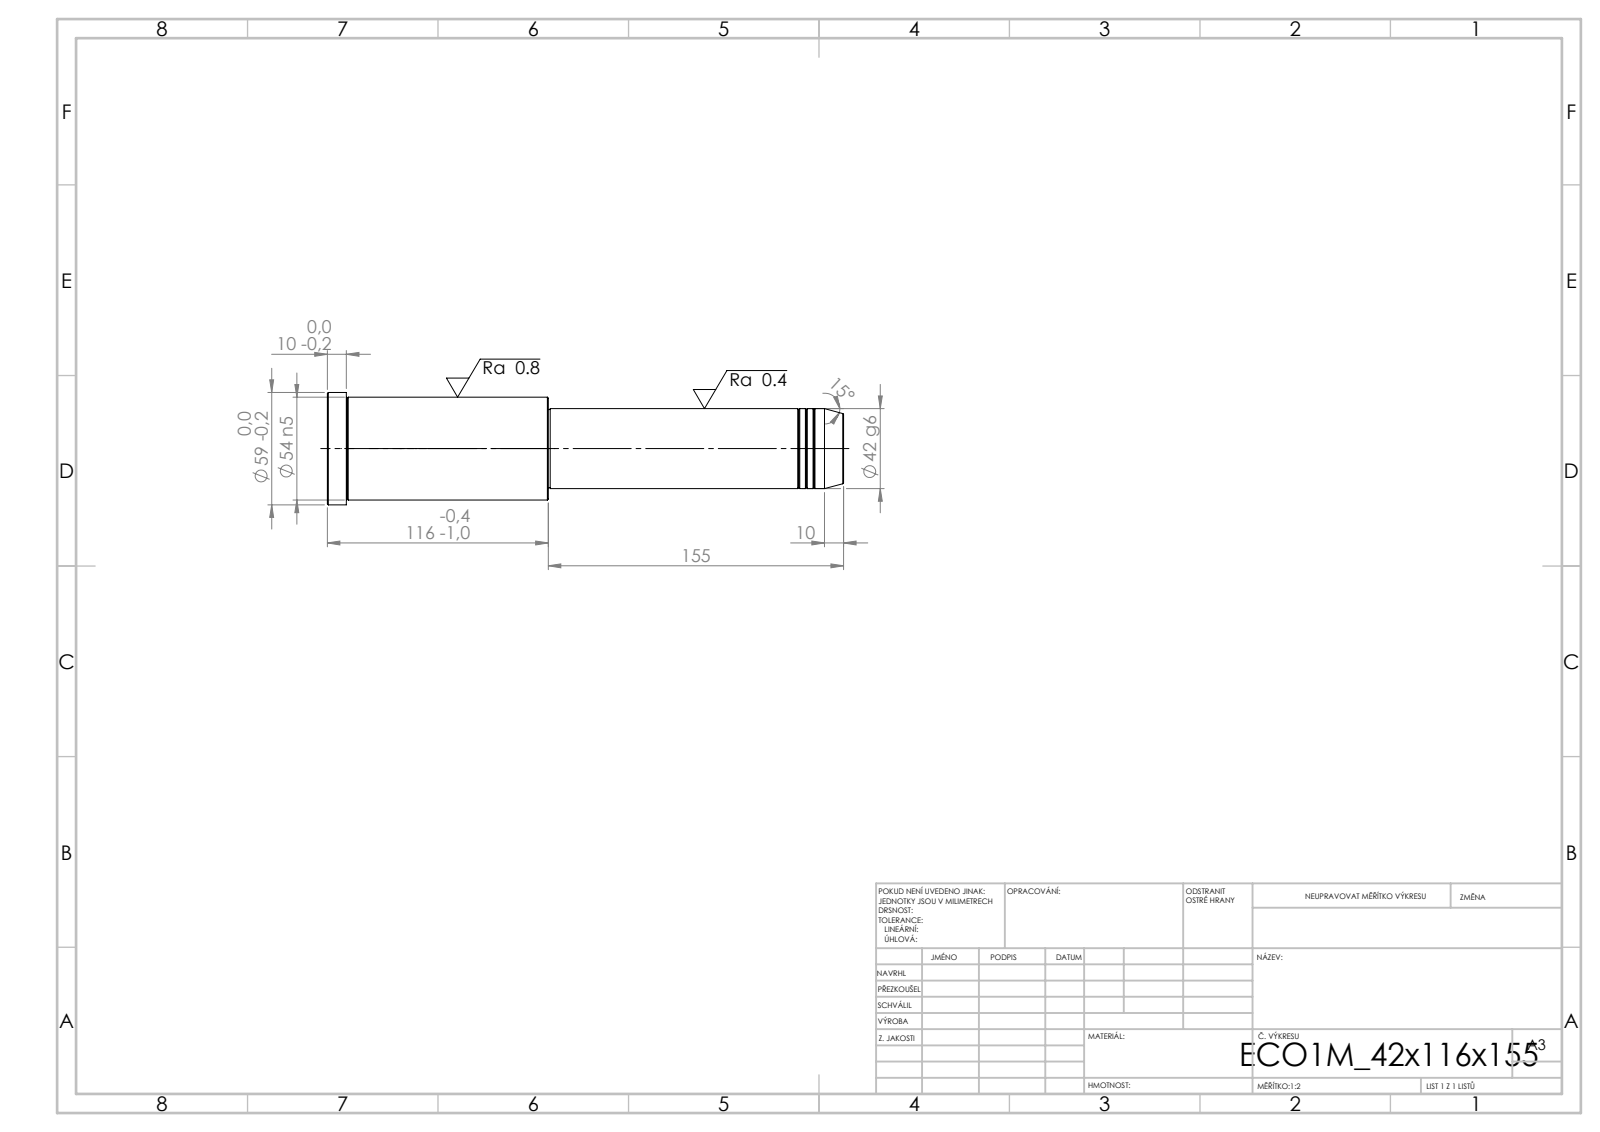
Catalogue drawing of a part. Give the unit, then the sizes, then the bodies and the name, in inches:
Units: inches
Overall size (bounding box): 10.669 × 2.323 × 2.323
Round bosses / shafts (diameter × count): ⌀2.323 ×1, ⌀2.126 ×1, ⌀1.654 ×1, ⌀1.614 ×1
Main face-to-face distances: 10.669, 6.102, 4.567, 10.276, 4.173, 0.394, 6.063, 0.039, 4.213, 4.606
Volume: 29.46 in³ · Surface area: 70.84 in²
Bodies: 1 solid, 43 faces (5 planar, 14 cylindrical, 24 other)
STEP written by: SolidWorks 2019 (CONFIG_CONTROL_DESIGN)
